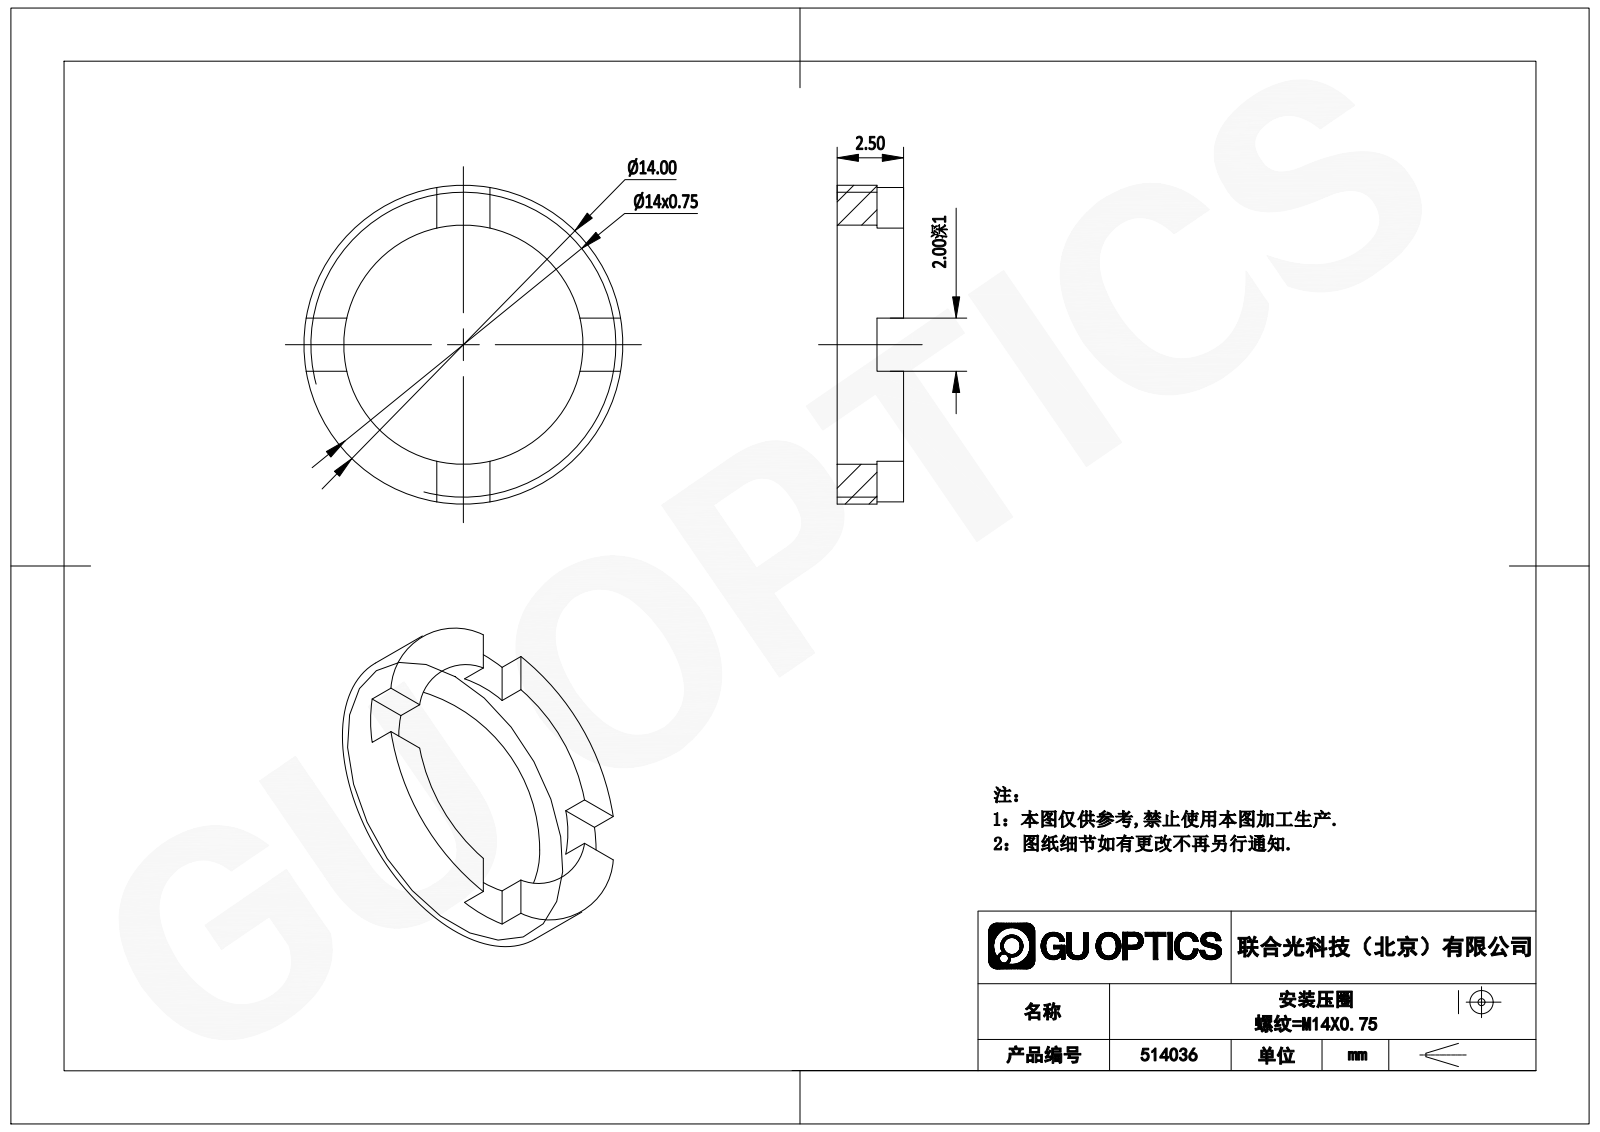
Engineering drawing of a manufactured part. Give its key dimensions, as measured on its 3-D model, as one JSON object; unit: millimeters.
{"part_name": "514036", "step_written_by": "SolidWorks 2020 (CONFIG_CONTROL_DESIGN)", "units": "millimeters", "bodies": {"solids": 1, "faces": 21, "planar": 17, "cylindrical": 4, "other": 0}, "overall_size": [14, 14, 2.5], "volume_mm3": 135, "surface_area_mm2": 310, "round_holes": [[11, 1]], "round_bosses_or_shafts": [[14, 1]], "face_to_face_distances": [2.5, 1.5, 1, 2]}
